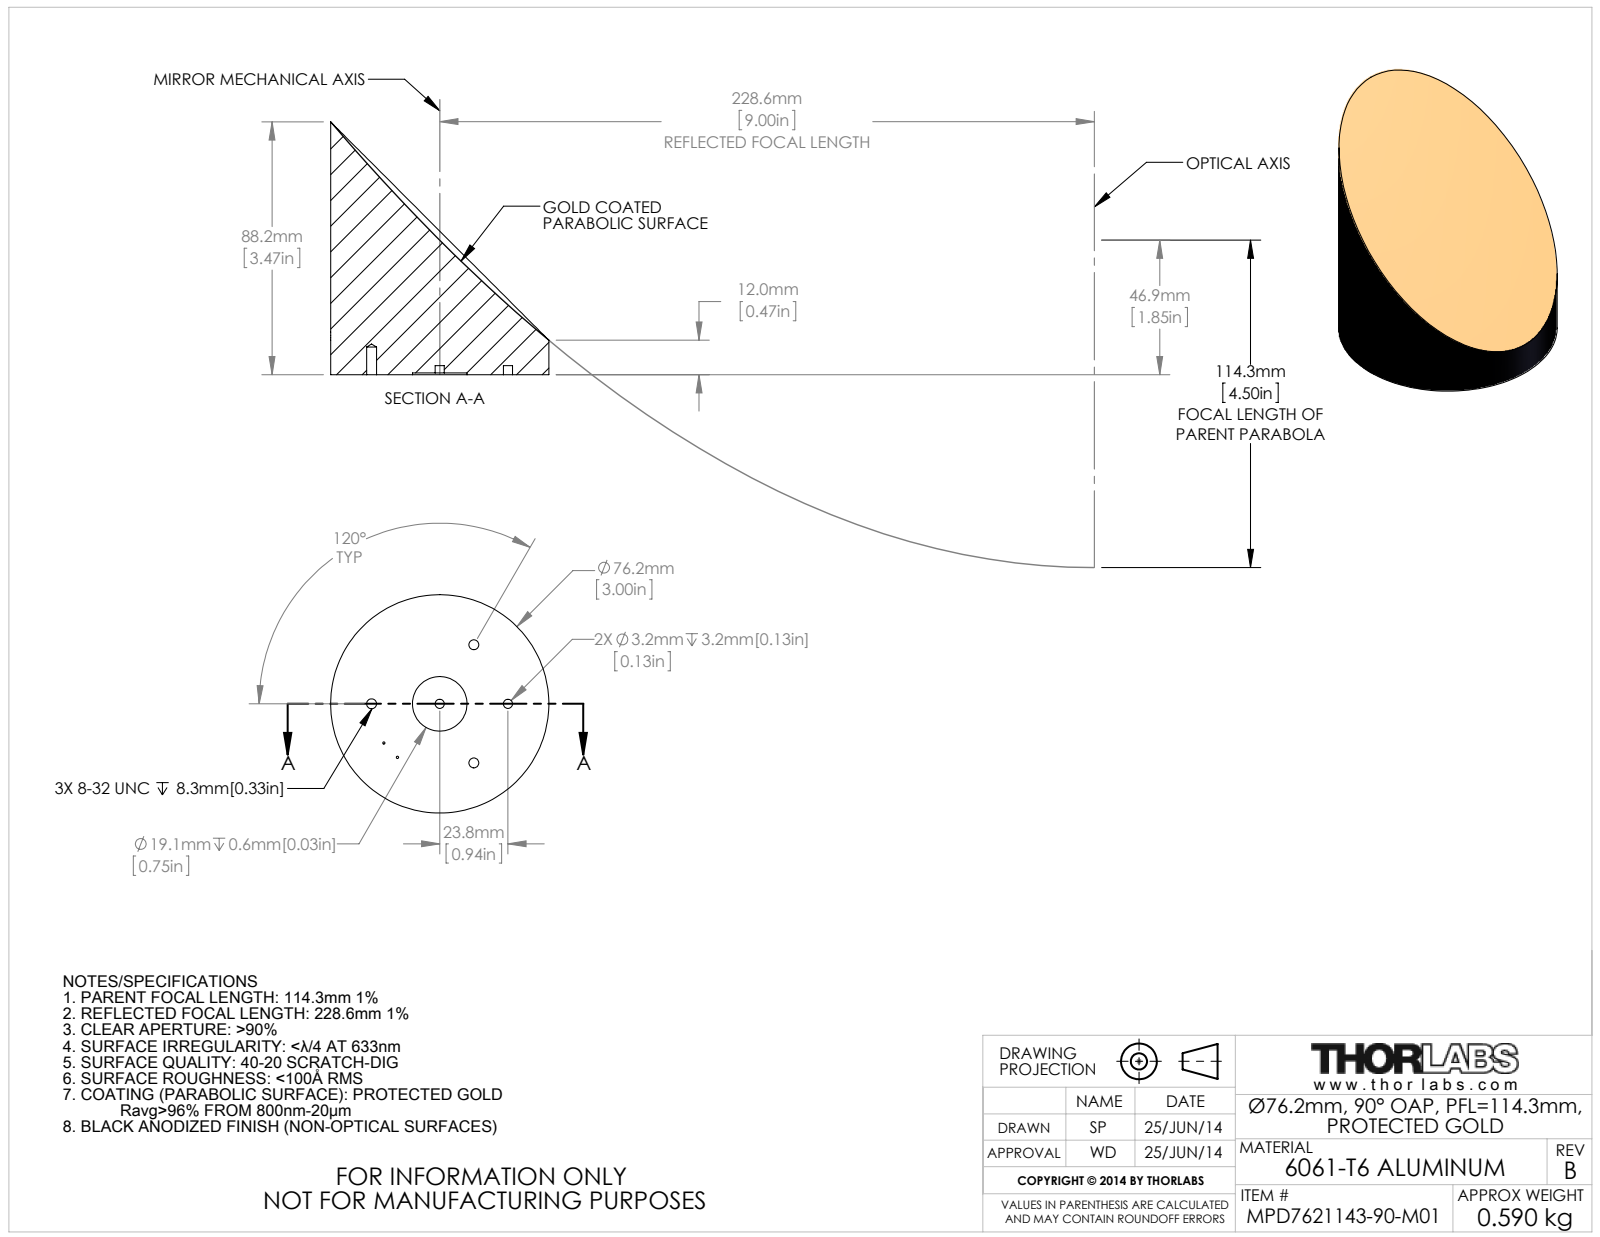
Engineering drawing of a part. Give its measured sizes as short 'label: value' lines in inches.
name: 24806-E0W
written by: SolidWorks 2014 (CONFIG_CONTROL_DESIGN)
unit: in
bodies: 1 solid, 67 faces (4 planar, 51 cylindrical, 12 other)
size: 3.473 × 3 × 3
volume: 13.47 in³; area: 36.33 in²
holes: 3× ⌀0.136, 2× ⌀0.126, 1× ⌀0.75
bosses: 1× ⌀3
face distances: 0.025, 0.125, 0.1
hole spacings: 0.937, 0.938, 1.624, 1.624, 1.875
